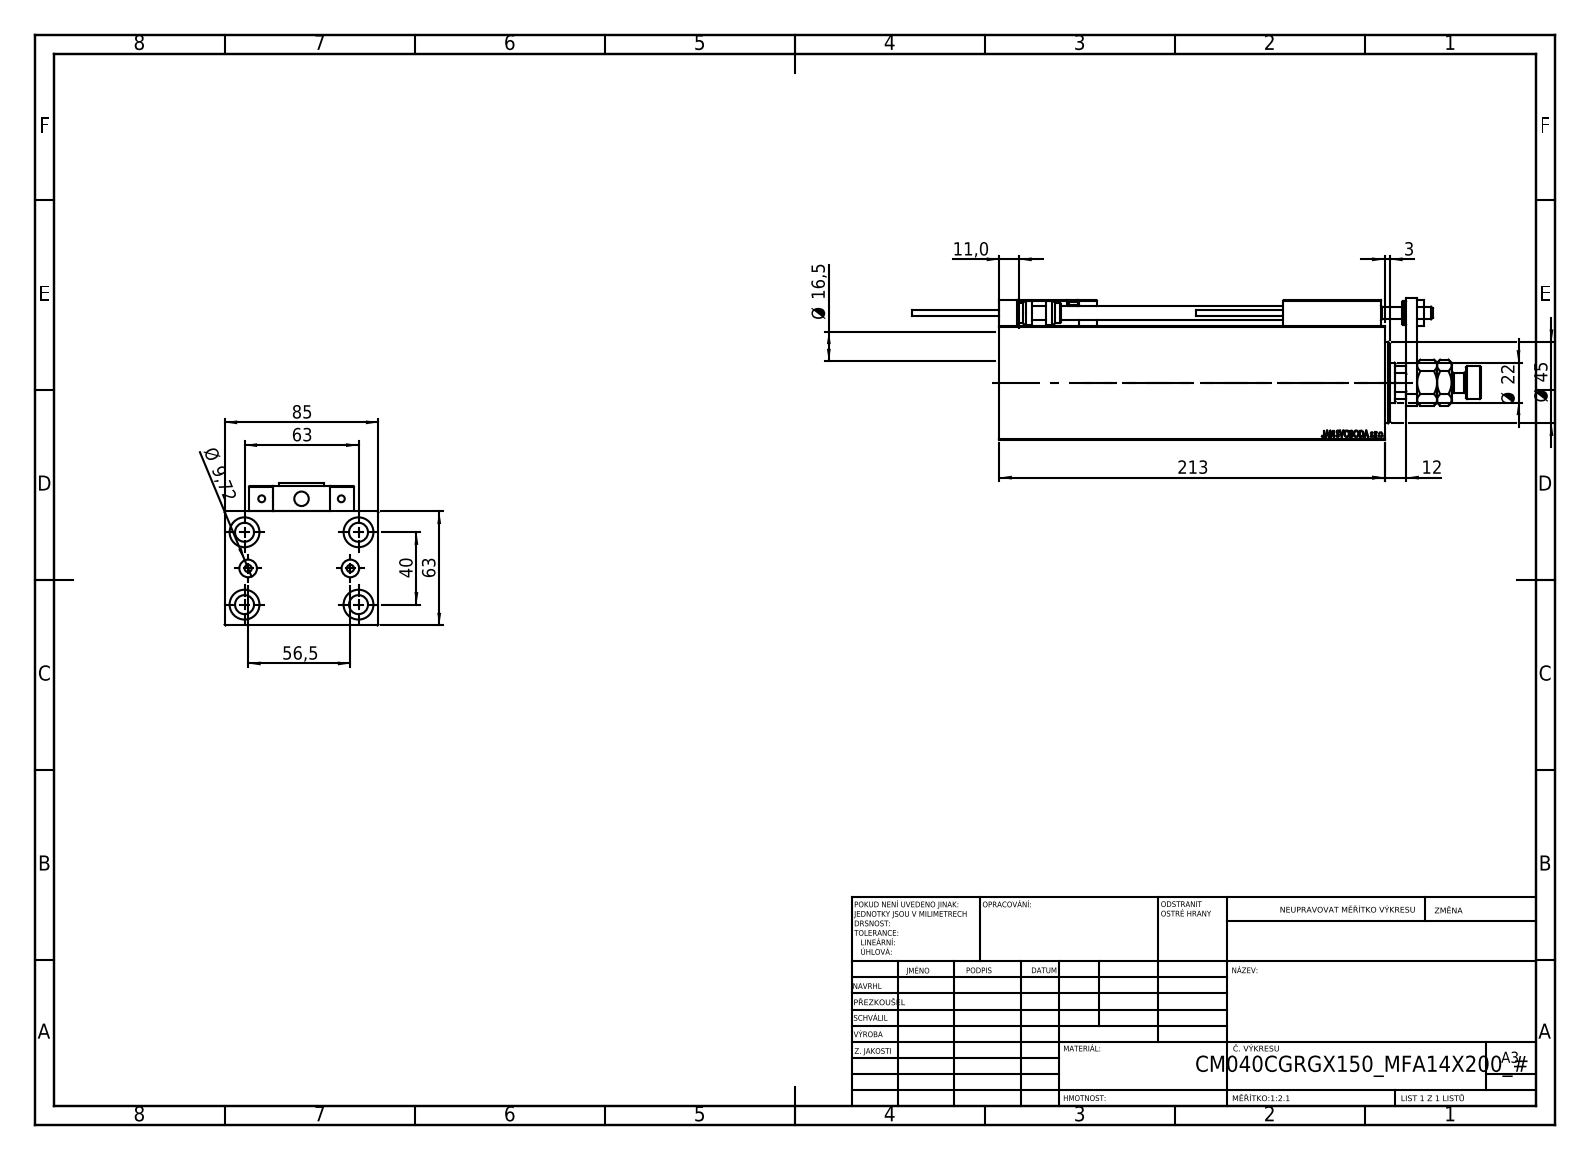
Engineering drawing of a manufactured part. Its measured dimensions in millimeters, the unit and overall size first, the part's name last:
Units: millimetres
Overall size (bounding box): 314 × 85 × 78.5
Round holes (diameter × count): ⌀4 ×6, ⌀8 ×5, ⌀16.5 ×5, ⌀3.2 ×4, ⌀10.5 ×4, ⌀5 ×2, ⌀9.72 ×2, ⌀7 ×1, ⌀12.5 ×1, ⌀22 ×1, ⌀25.5 ×1, ⌀40 ×1
Round bosses / shafts (diameter × count): ⌀11 ×2, ⌀5 ×2, ⌀3.8 ×2, ⌀18 ×1, ⌀13 ×1
Partial cylindrical surfaces — rounded edges, fillets, slot ends (radius × count): R0.3 ×30, R3 ×2, R10.5 ×1
Main face-to-face distances: 63, 85, 12, 201, 213, 14, 18, 30, 77, 20
Hole centre spacings: 37.31, 11.37, 20, 20.1, 20.5, 29.59, 29.69, 36.06
Volume: 988 150 mm³ · Surface area: 190 233 mm²
Bodies: 24 solids, 1330 faces (576 planar, 188 cylindrical, 566 other)
Part name (STEP PRODUCT): V450CM_C_VCP; V450CM_C_Body; MAGNET; SWITCH_X_FRONT_BACK (+8 more)
STEP written by: SolidWorks 2019 (CONFIG_CONTROL_DESIGN)
